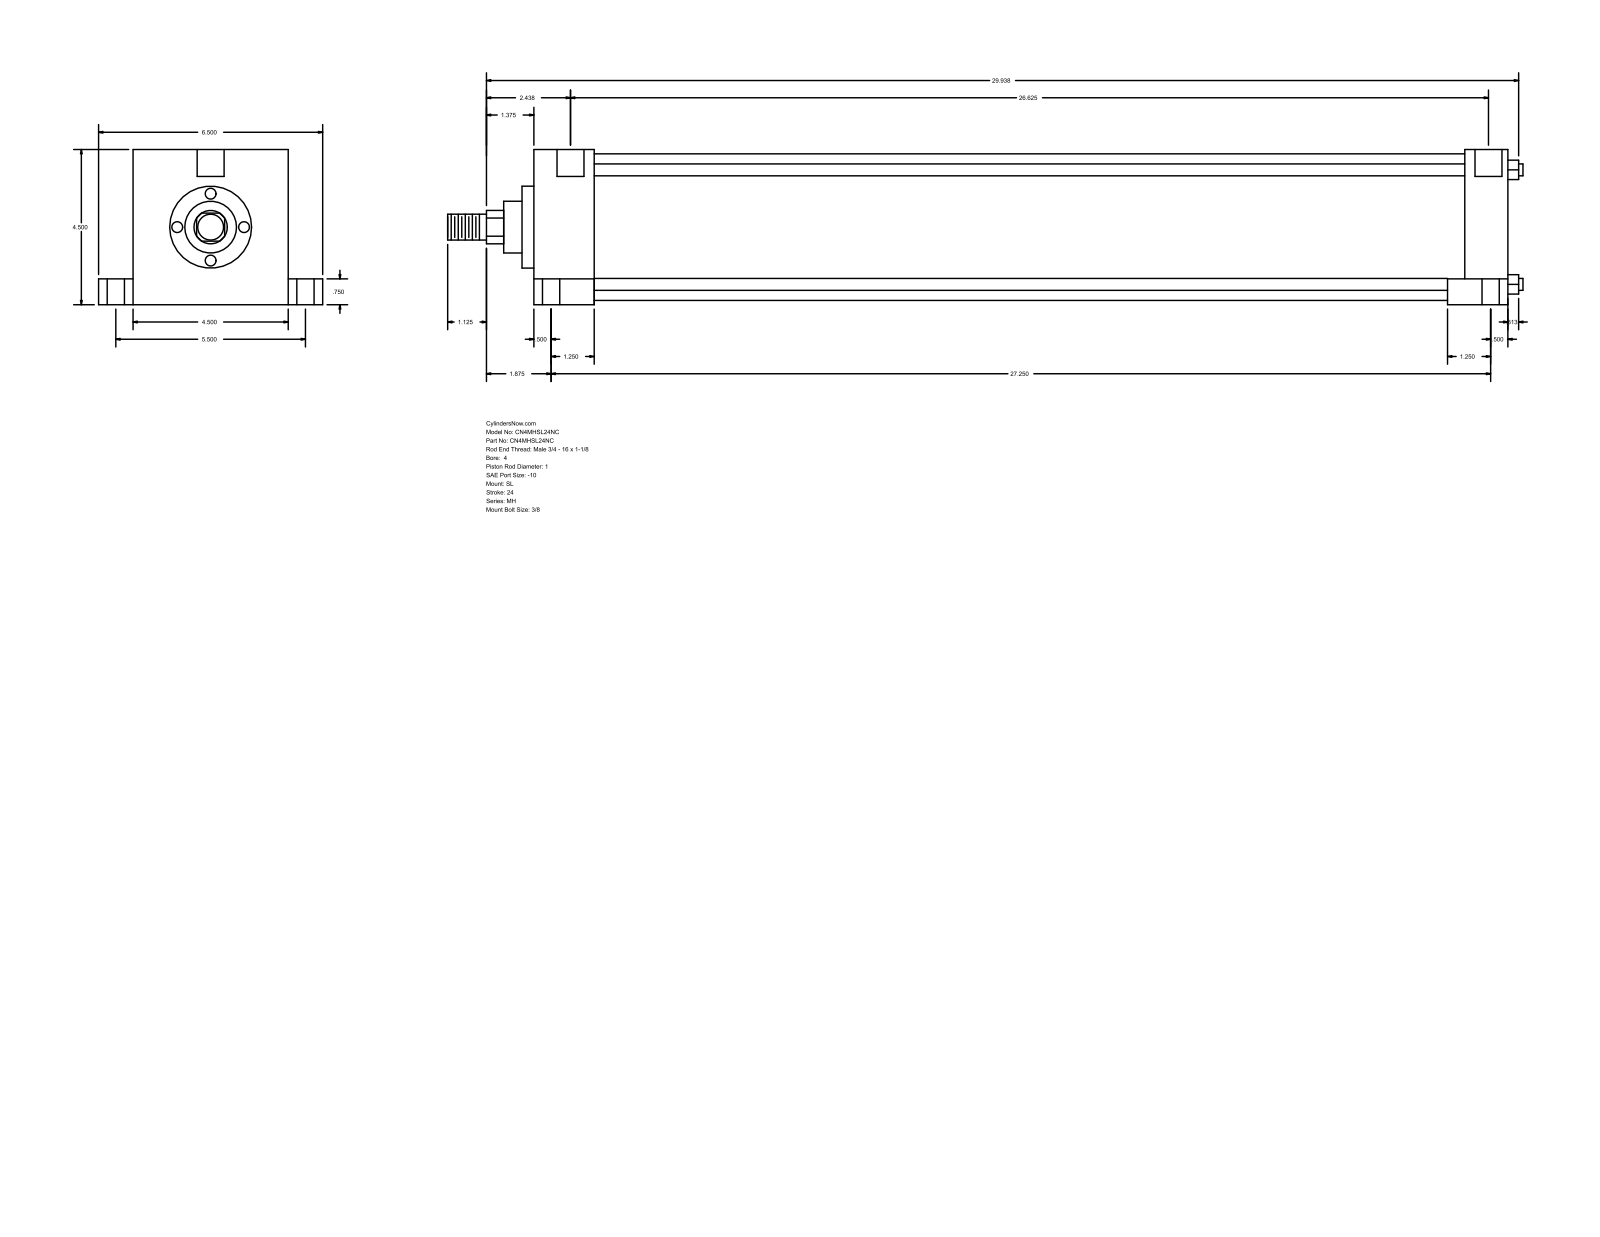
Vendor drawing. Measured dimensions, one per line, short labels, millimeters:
name: MH_SL__0400_1
written by: GSSL Pune (CONFIG_CONTROL_DESIGN)
unit: mm
bodies: 0 solids, 110 faces (77 planar, 33 cylindrical, 0 other)
size: 792.16 × 165.1 × 114.3
holes: 4× ⌀8.73, 4× ⌀12.7, 4× ⌀19.05, 2× ⌀19.84
bosses: 4× ⌀8.76, 1× ⌀107.95, 1× ⌀60.33, 1× ⌀38.1, 1× ⌀25.4, 1× ⌀19.05
rounds: 1× R12.29
face distances: 114.3, 717.56, 44.46, 673.1, 685.81, 641.35, 31.75, 25.4, 139.7, 19.05
hole spacings: 1.58, 69.85, 69.87, 71, 71.3, 139.7, 677.86, 679.44
